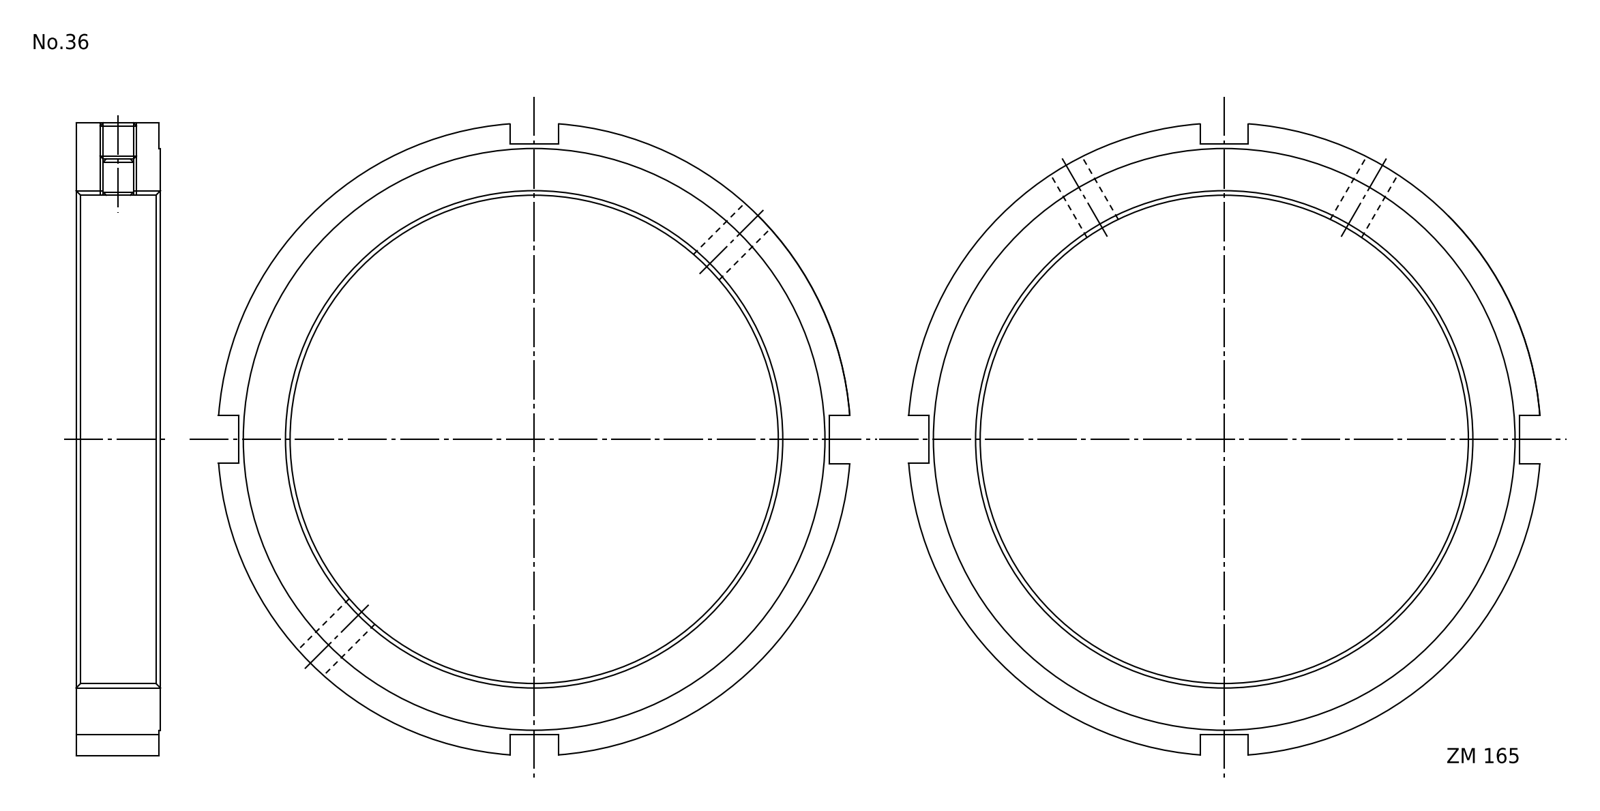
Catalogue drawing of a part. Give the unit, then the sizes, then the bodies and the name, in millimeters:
Units: millimetres
Overall size (bounding box): 209.39 × 209.39 × 28
Round holes (diameter × count): ⌀10.11 ×2, ⌀165 ×1
Round bosses / shafts (diameter × count): ⌀210 ×1, ⌀193 ×1
Main face-to-face distances: 28, 0.5, 27.5, 90, 106, 196, 16
Volume: 352 660 mm³ · Surface area: 61 164 mm²
Bodies: 1 solid, 23 faces (15 planar, 8 cylindrical, 0 other)
Part name (STEP PRODUCT): FKD ZM165
STEP written by: Autodesk Inventor 2011 (AUTOMOTIVE_DESIGN)
